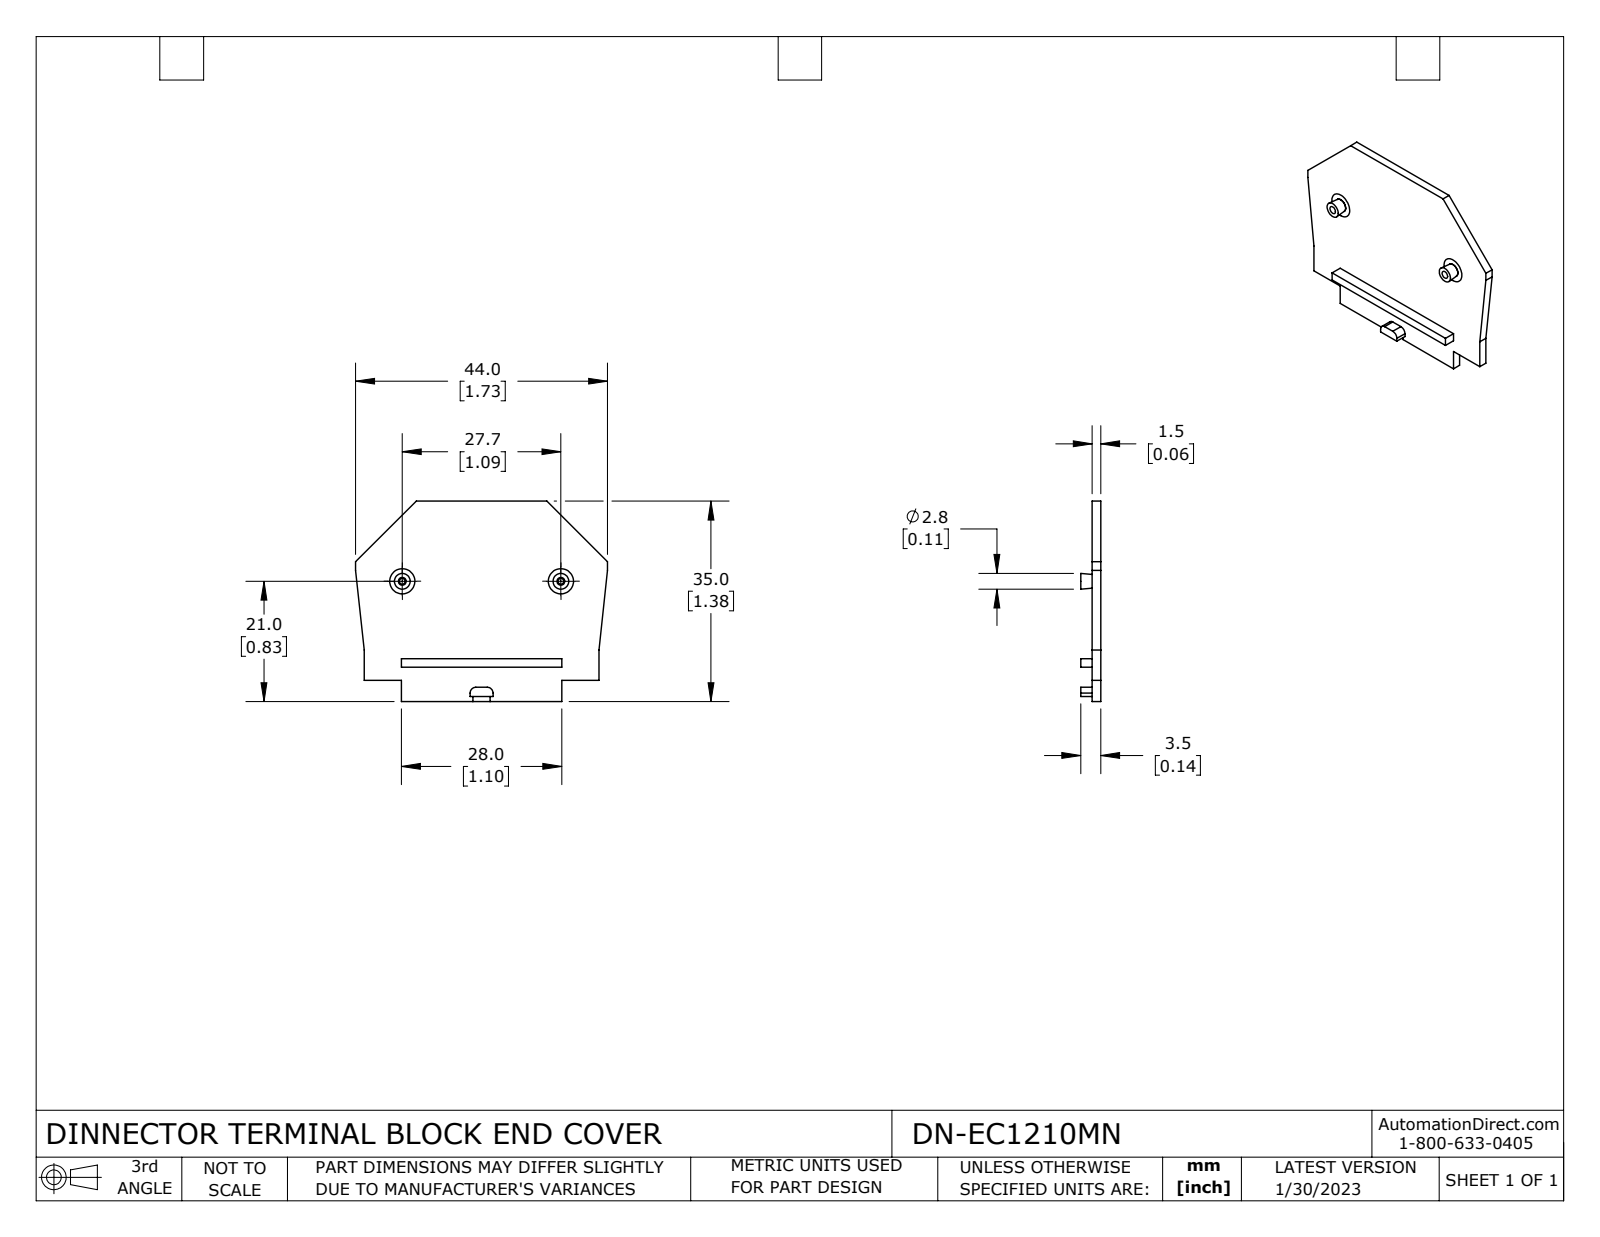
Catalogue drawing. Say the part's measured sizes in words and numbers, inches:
The part is named "DN-EC1210MN". Its 3-D file was written by "SolidWorks 2021 (CONFIG_CONTROL_DESIGN)". It is 1 solid with 51 faces: 33 planar, 2 cylindrical and 16 other. Overall it measures 1.732 by 1.378 by 0.138 inches. Its volume is 0.128 cubic inches and its surface area 4.771 square inches. Partial cylindrical surfaces (rounded edges, fillets, slot ends): 2 of radius 0.039. The main face-to-face distances are 0.059, 0.138, 0.079, 0.236, 0.295, 1.378, 1.142, 1.083, 0.146, 0.091.
